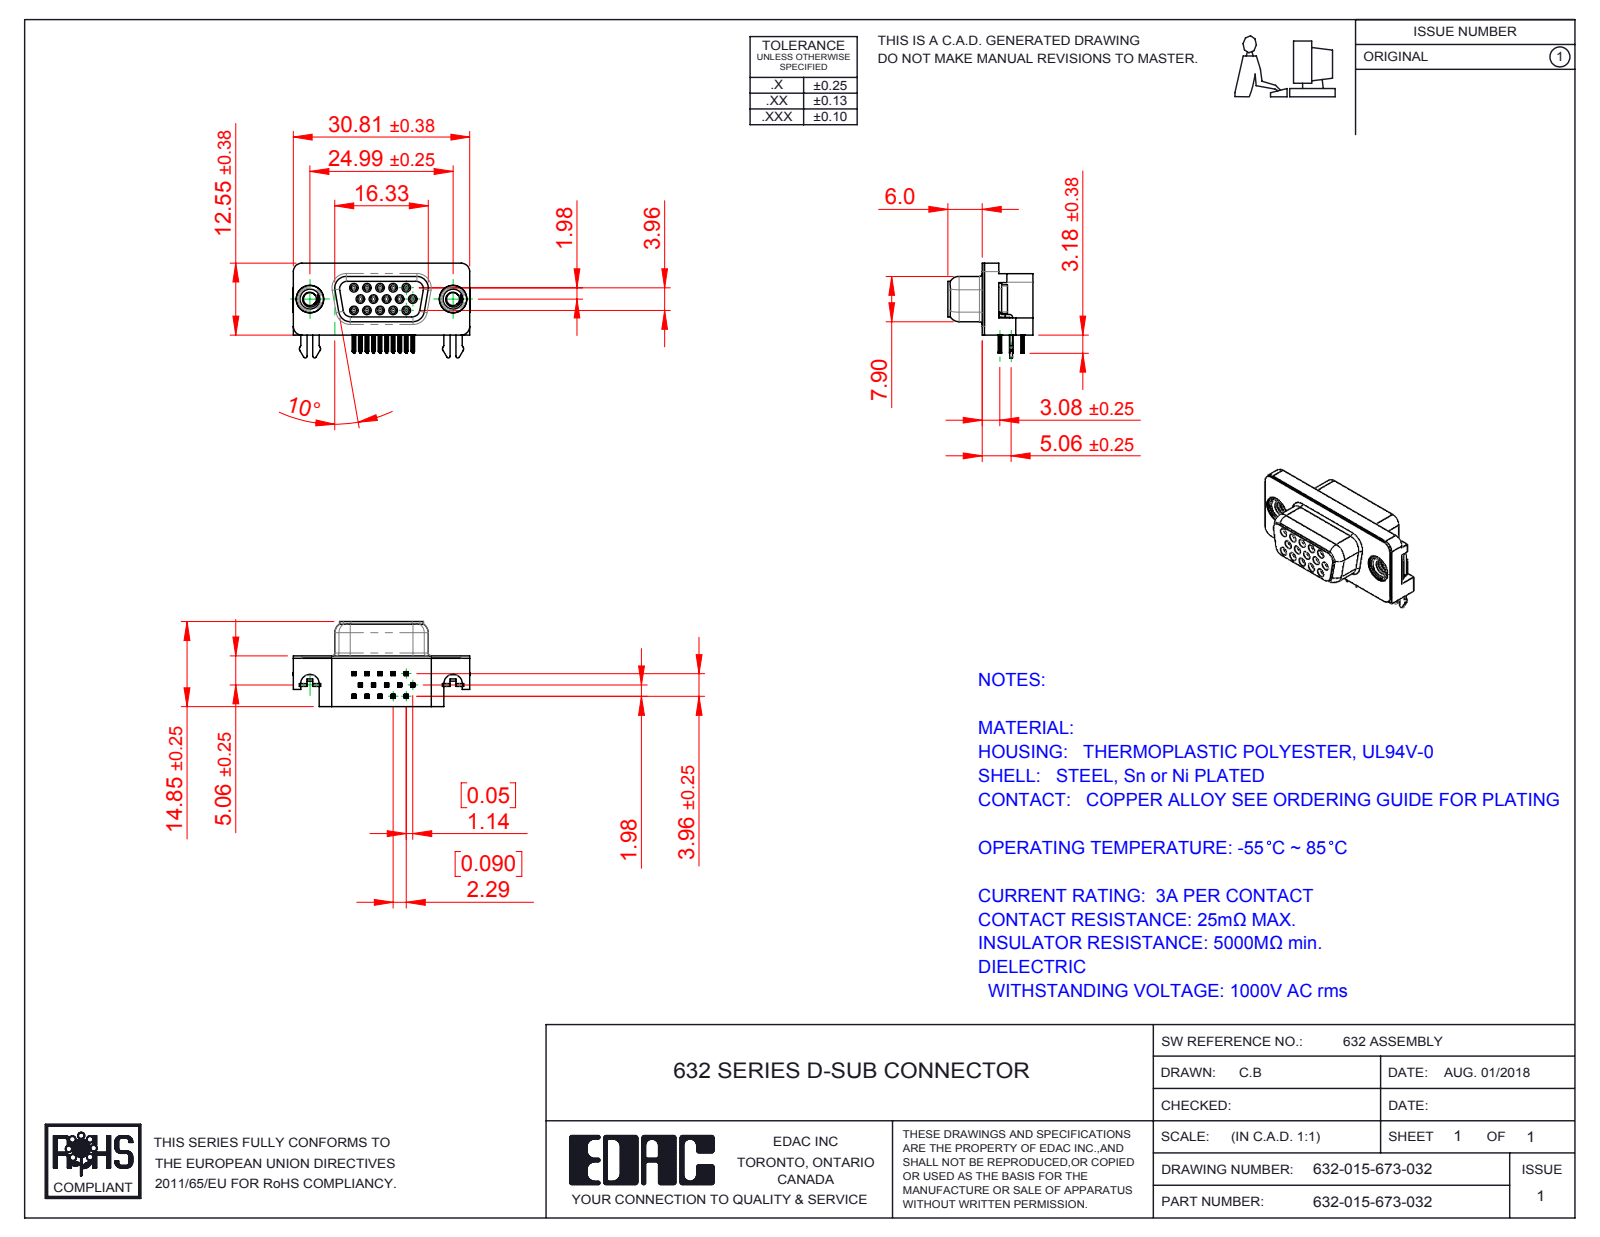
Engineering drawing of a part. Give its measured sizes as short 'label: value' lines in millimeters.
name: 632 Contact Middle; 632 Housing_15 Socket; 632 Contact Bottom; 632 2 Prong Board Lock (+5 more)
written by: SolidWorks 2016 (CONFIG_CONTROL_DESIGN)
unit: mm
bodies: 21 solids, 2338 faces (990 planar, 612 cylindrical, 736 other)
size: 30.89 × 16.55 × 14.85
volume: 2 921 mm³; area: 5 015 mm²
holes: 15× ⌀0.8, 15× ⌀0.9, 2× ⌀2.26, 2× ⌀4, 2× ⌀4.8, 2× ⌀5
bosses: 15× ⌀1.2, 2× ⌀4.9, 2× ⌀4.75, 2× ⌀3.9
rounds: 120× R0.1, 60× R0.15, 30× R0.35, 15× R0.34, 11× R1, 10× R0.28, 10× R0.5, 8× R0.25
face distances: 0.4, 1.98, 8.45, 8.85, 2.9, 2.5, 5.95, 6.4, 6.7, 7.05
hole spacings: 2.28, 2.29, 3.96, 4.57, 6.05, 3.97, 4.58, 6.86
